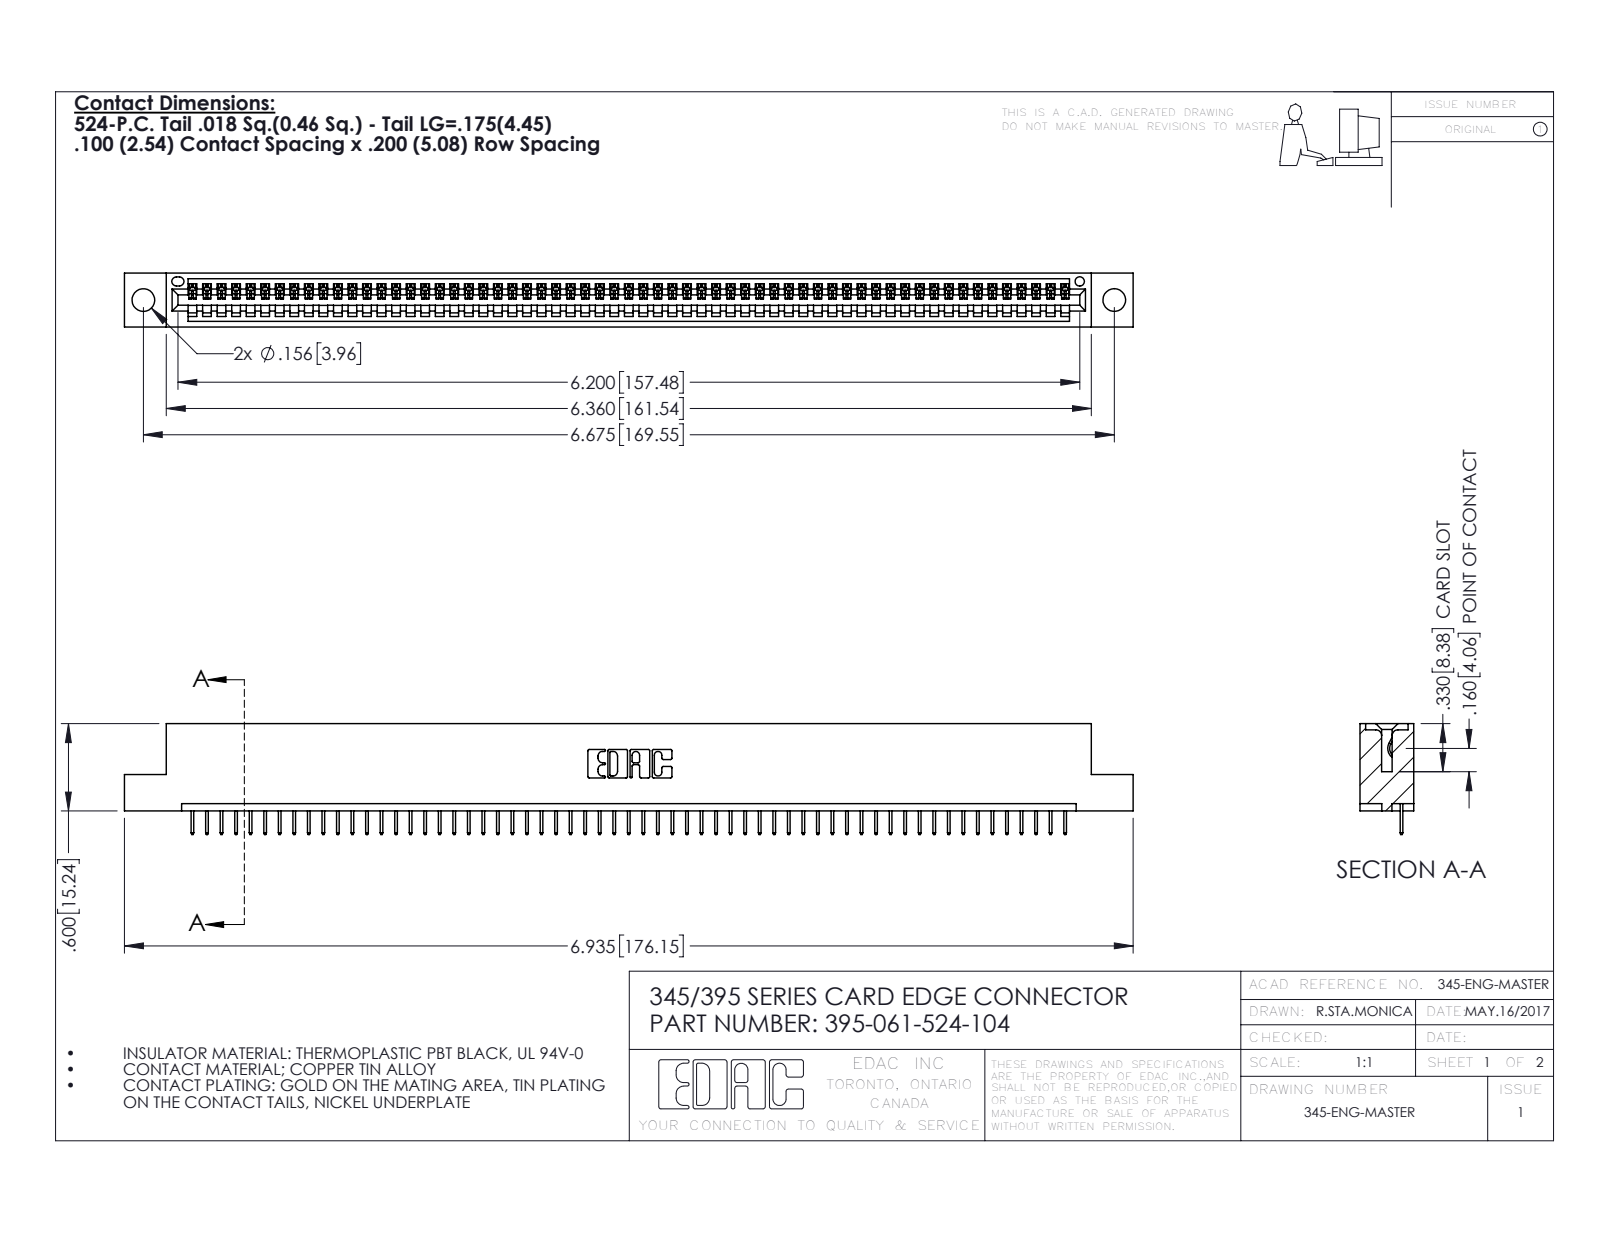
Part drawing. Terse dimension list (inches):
name: 345 Part_Flush Mounting Lugs - 0.156 Dia-TH; 345-292-001_345-293-124; 395-061-524-104
written by: SolidWorks 2016 (CONFIG_CONTROL_DESIGN)
unit: in
bodies: 62 solids, 3908 faces (2886 planar, 1022 cylindrical, 0 other)
size: 6.935 × 0.762 × 0.37
volume: 1.01 in³; area: 33.02 in²
holes: 2× ⌀0.156, 1× ⌀0.064
rounds: 122× R0.006, 22× R0.01, 6× R0.007, 6× R0.031, 3× R0.026, 2× R0.031, 2× R0.04, 1× R0.014
face distances: 0.298, 0.072, 0.37, 0.2, 0.098, 0.272, 0.025, 0.225, 0.072, 0.149
hole spacings: 0.27, 6.439, 6.675
